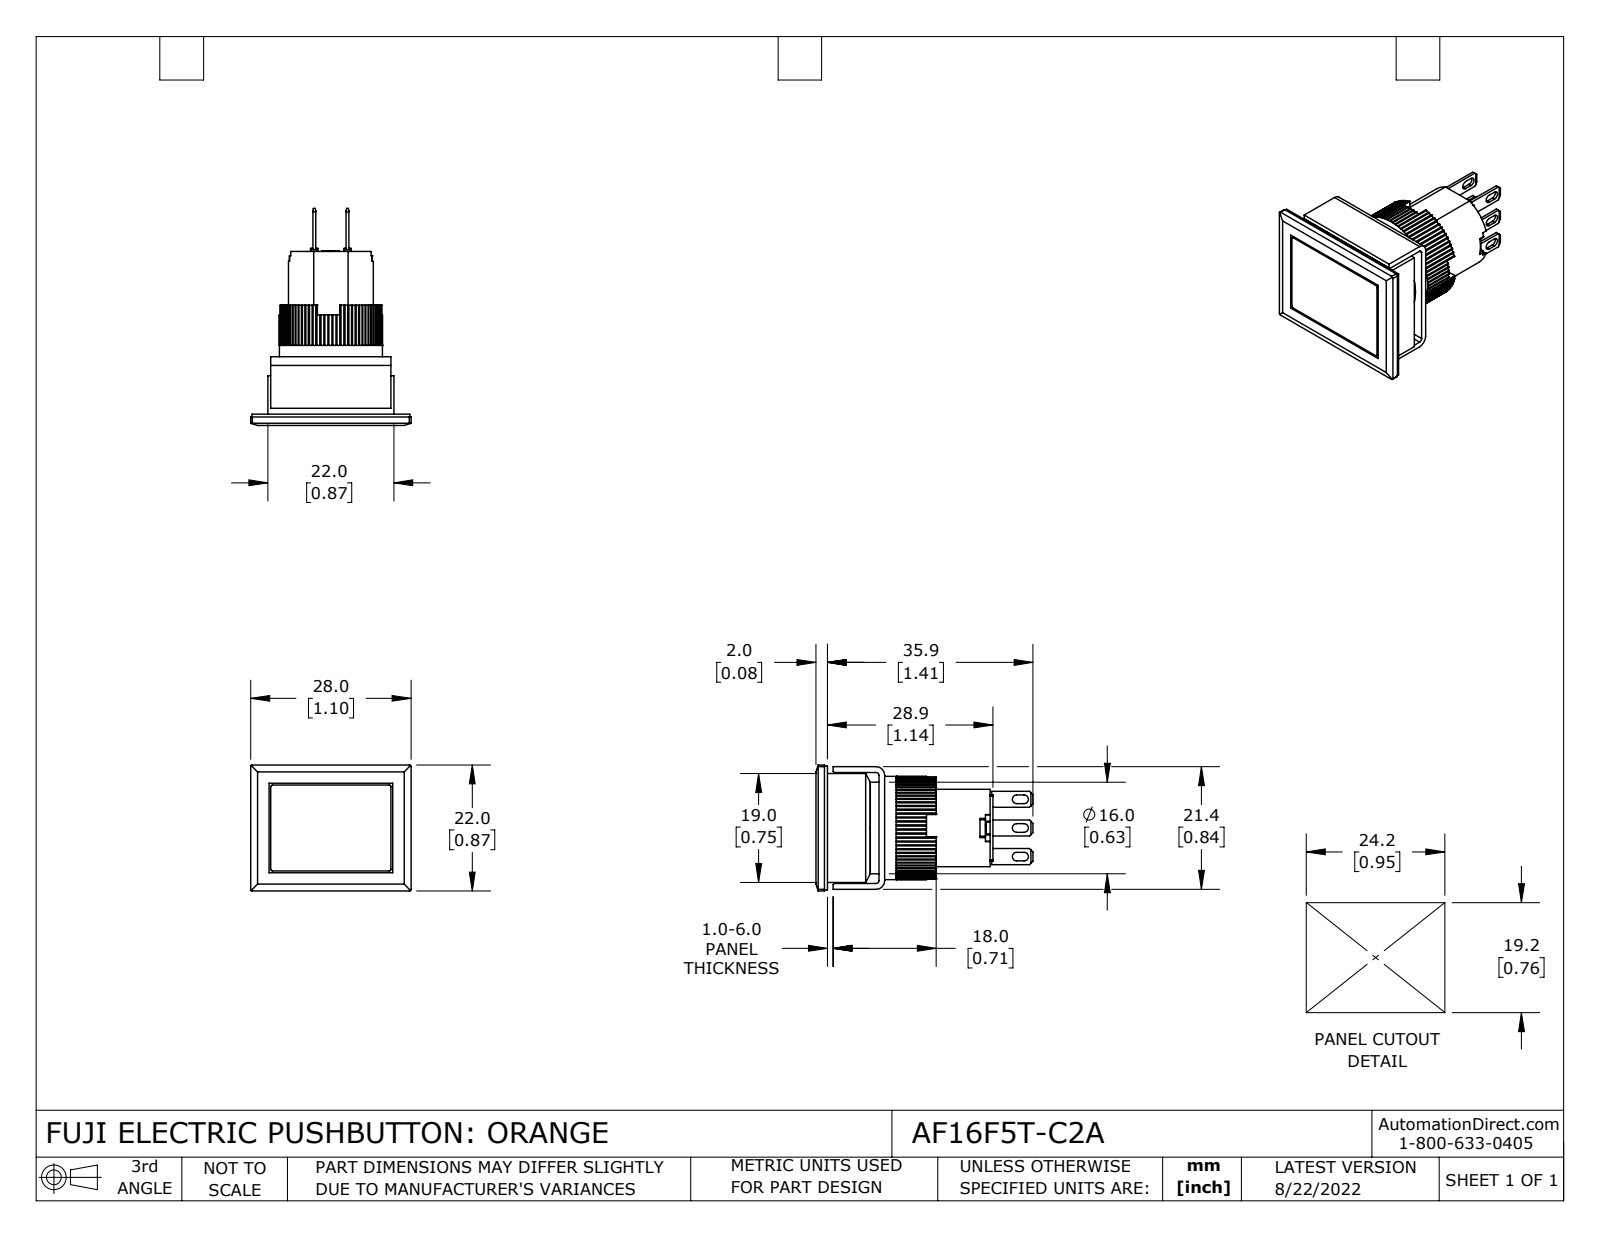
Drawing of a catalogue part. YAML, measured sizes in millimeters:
part_name: "AF16F5T-C2A"
step_written_by: "SolidWorks 2021 (CONFIG_CONTROL_DESIGN)"
units: millimeters
bodies: {solids: 12, faces: 798, planar: 620, cylindrical: 176, other: 2}
overall_size: [37.9, 28, 22]
volume: 8870
surface_area: 7645
round_holes:
  - {diameter: 1, count: 1}
  - {diameter: 18, count: 1}
round_bosses_or_shafts:
  - {diameter: 16, count: 1}
  - {diameter: 14.8, count: 1}
partial_cylinders:
  - {radius: 0.3, count: 80}
  - {radius: 0.2, count: 12}
  - {radius: 0.3, count: 8}
  - {radius: 0.8, count: 6}
  - {radius: 0.5, count: 2}
  - {radius: 1.5, count: 2}
face_to_face_distances: [9.5, 1.5, 0.5, 3.6, 1, 8, 5.9, 2.1, 2, 19.2]
